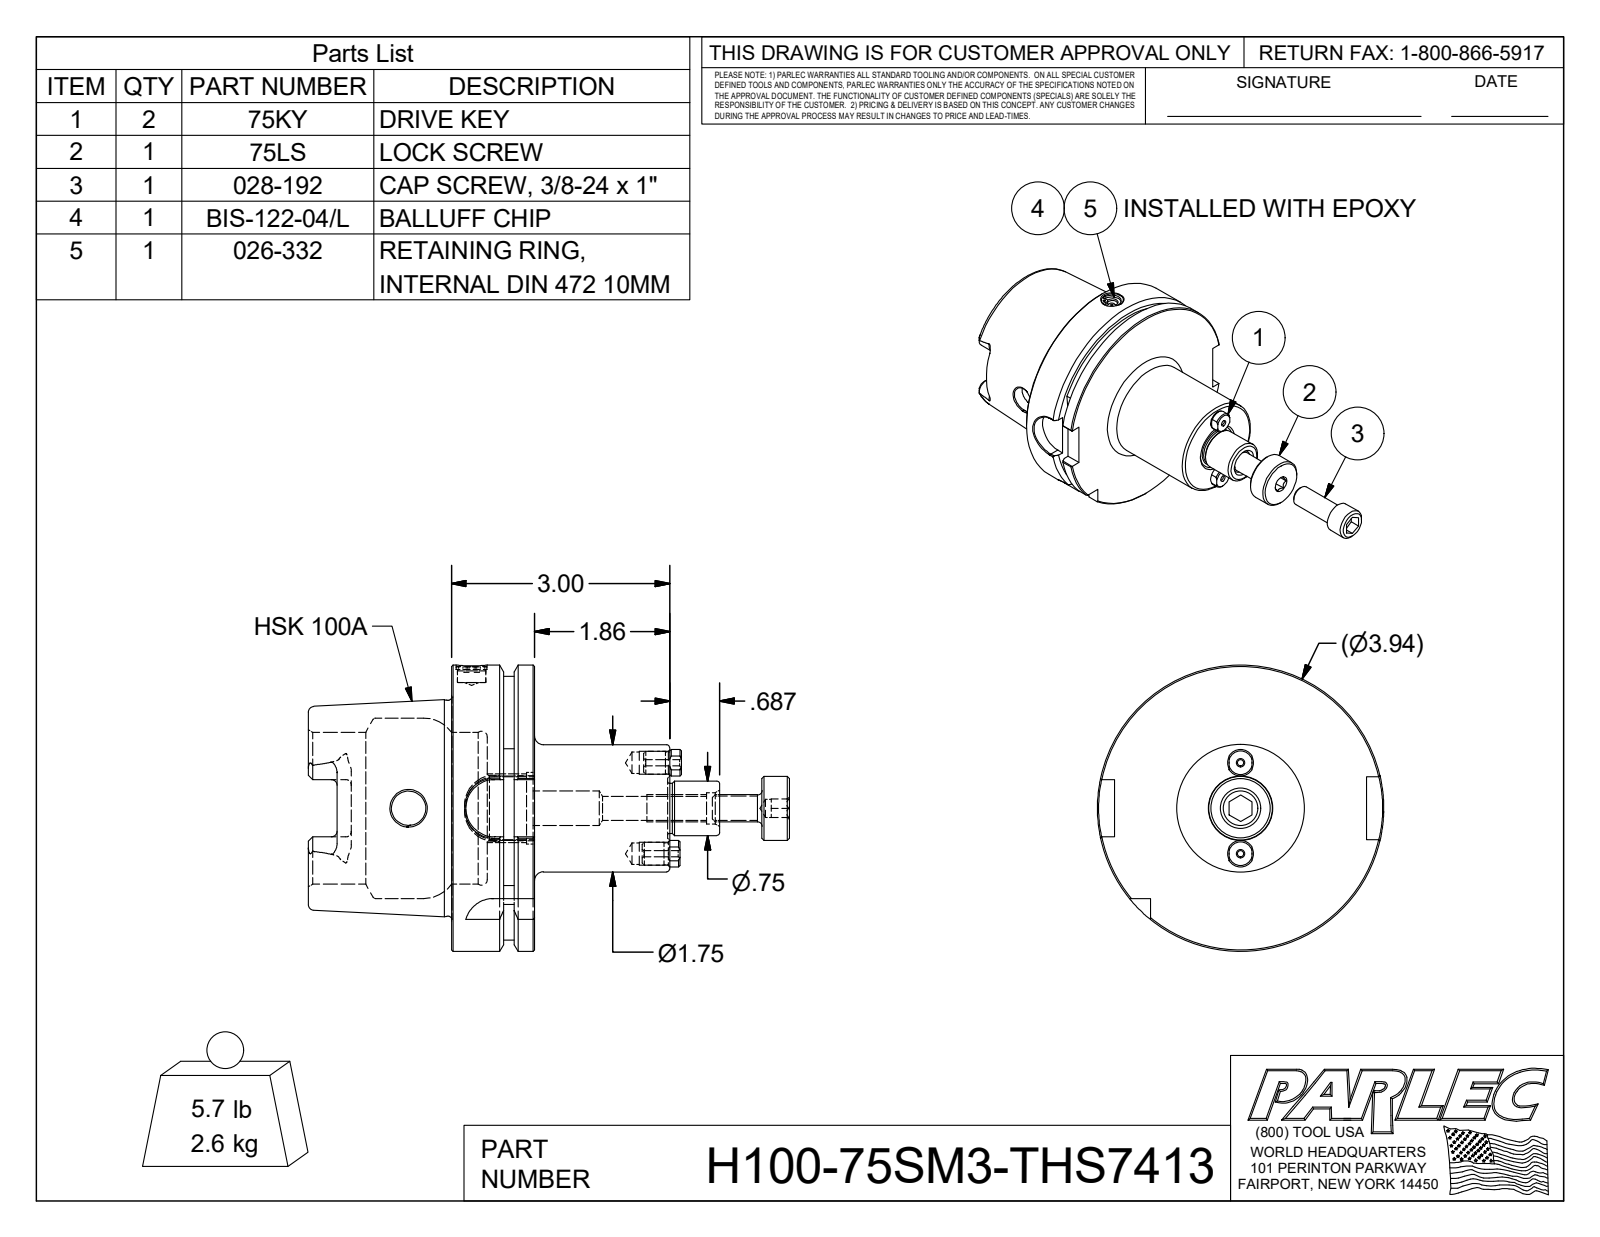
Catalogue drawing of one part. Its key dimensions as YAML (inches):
part_name: "H100-75SM3; 028-192; 75KY"
step_written_by: "Autodesk Inventor 2012 (AUTOMOTIVE_DESIGN)"
units: inches
bodies: {solids: 4, faces: 193, planar: 69, cylindrical: 52, other: 72}
overall_size: [7.608, 3.937, 3.937]
volume: 20.39
surface_area: 98.2
round_holes:
  - {diameter: 0.084, count: 2}
  - {diameter: 0.3, count: 2}
  - {diameter: 0.312, count: 2}
  - {diameter: 0.472, count: 2}
  - {diameter: 0.33, count: 1}
  - {diameter: 0.394, count: 1}
  - {diameter: 0.43, count: 1}
  - {diameter: 0.881, count: 1}
  - {diameter: 0.985, count: 1}
  - {diameter: 2.087, count: 1}
  - {diameter: 2.48, count: 1}
round_bosses_or_shafts:
  - {diameter: 0.318, count: 2}
  - {diameter: 3.937, count: 1}
  - {diameter: 2.967, count: 1}
  - {diameter: 1.75, count: 1}
  - {diameter: 0.75, count: 1}
  - {diameter: 0.69, count: 1}
  - {diameter: 0.556, count: 1}
  - {diameter: 0.375, count: 1}
partial_cylinders:
  - {radius: 0.079, count: 6}
  - {radius: 0.192, count: 4}
  - {radius: 0.394, count: 4}
  - {radius: 0.183, count: 2}
  - {radius: 1.811, count: 1}
face_to_face_distances: [1.142, 0.492, 0.65, 3.12, 2.628, 1.978, 1.969, 2.461, 3.11, 5.089]
hole_center_spacings: [0.625, 0.625, 1.25, 1.25]
